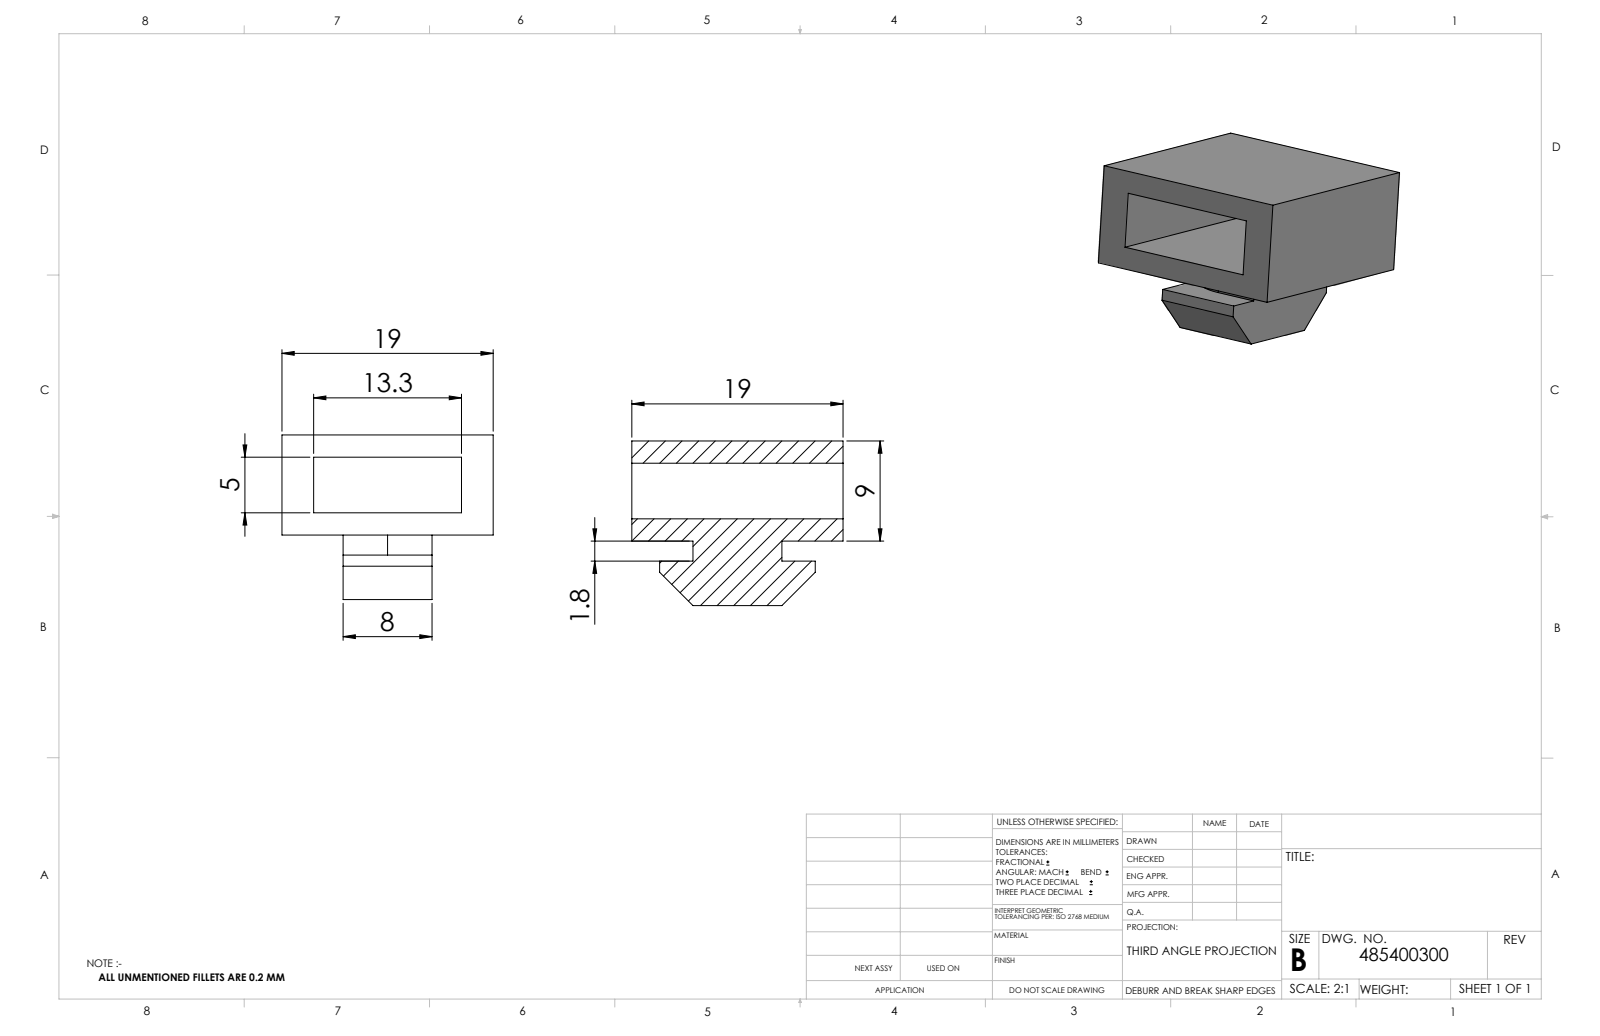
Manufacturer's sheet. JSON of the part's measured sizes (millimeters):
{"part_name": "485400300_c_1", "step_written_by": "SolidWorks 2014 (CONFIG_CONTROL_DESIGN)", "units": "millimeters", "bodies": {"solids": 1, "faces": 23, "planar": 21, "cylindrical": 2, "other": 0}, "overall_size": [19, 19, 14.8], "volume_mm3": 2464, "surface_area_mm2": 2259, "partial_cylinders_radius": [[4, 1]], "face_to_face_distances": [2, 7, 9, 19, 5, 2.85, 16.15, 5.5, 13.5, 2.65]}
